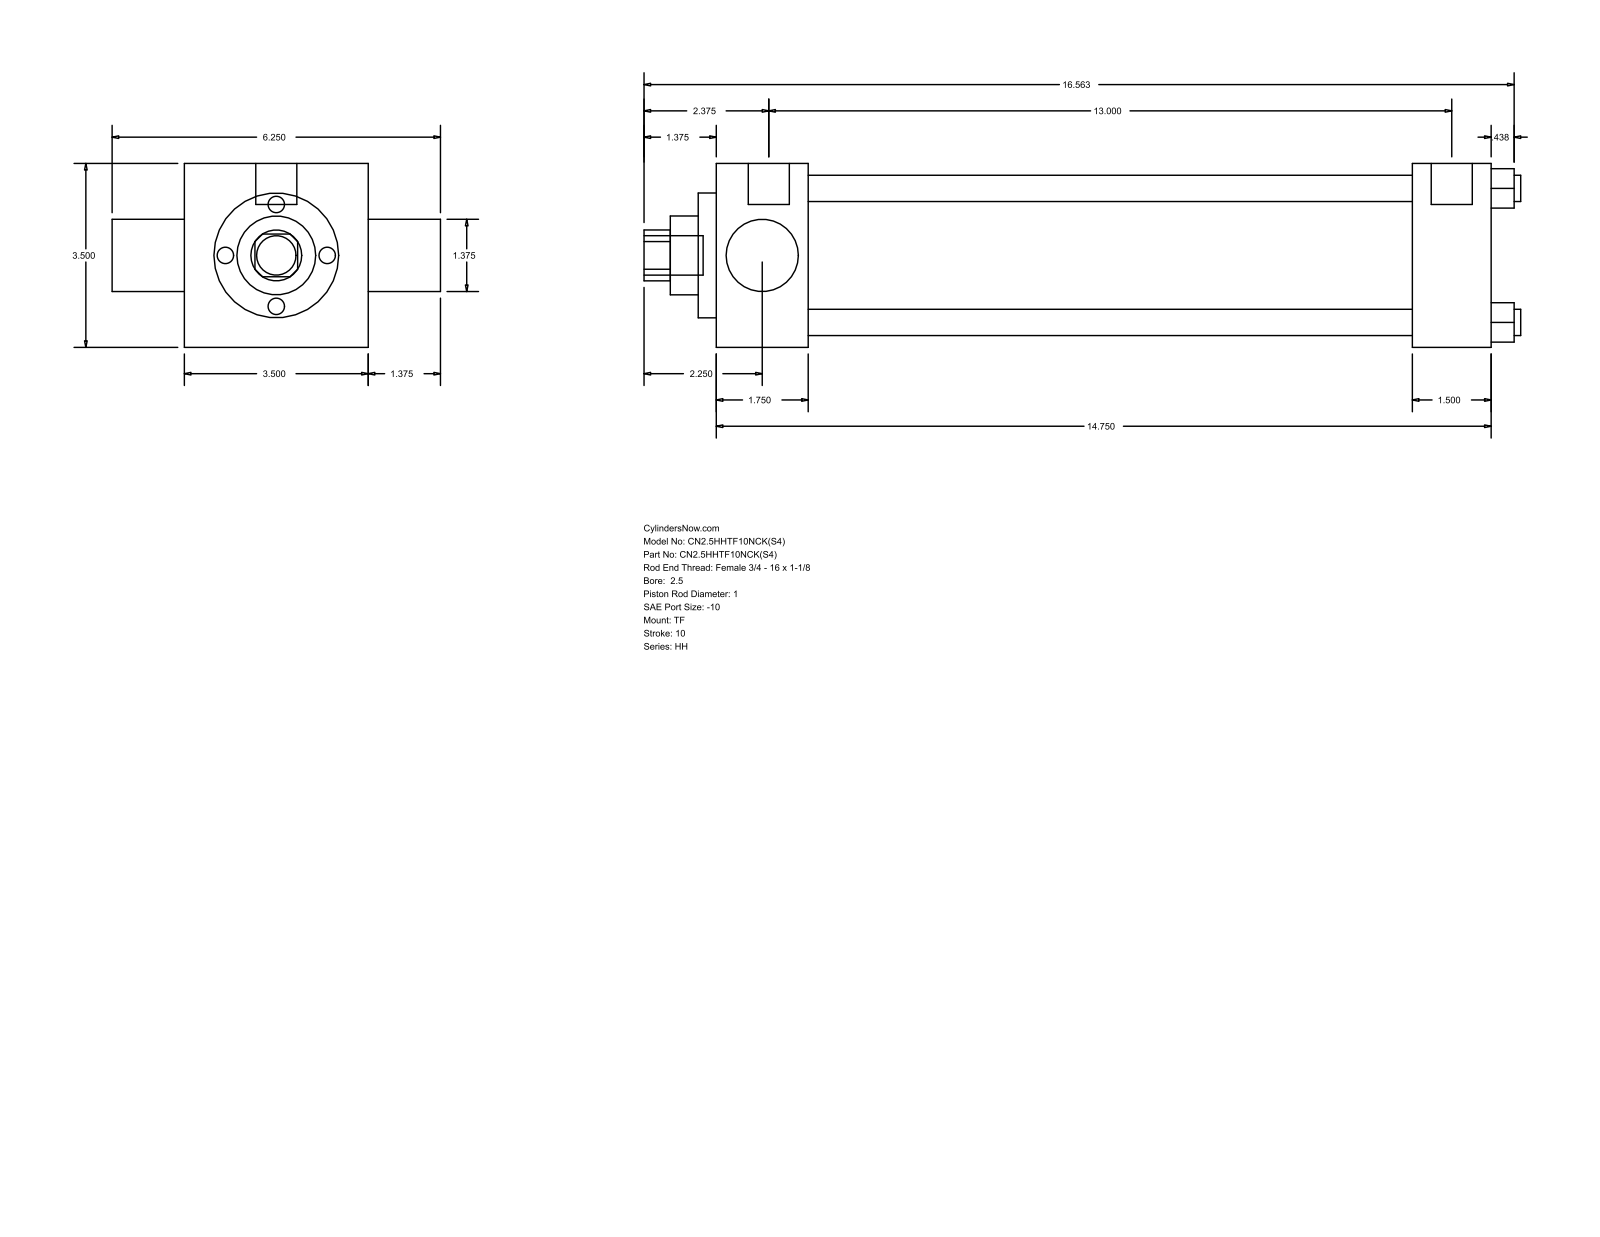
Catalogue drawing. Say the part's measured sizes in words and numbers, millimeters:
The part is named "HH_TF__0250_1". Its 3-D file was written by "GSSL Pune (CONFIG_CONTROL_DESIGN)". It is 0 solids with 86 faces: 61 planar, 25 cylindrical and 0 other. Overall it measures 423.86 by 158.75 by 88.9 millimeters. Round holes: 4 of diameter 12.7, 1 of diameter 25.4, 1 of diameter 34.92, 1 of diameter 38.1, 1 of diameter 60.33, 1 of diameter 73.03. Round bosses or shafts: 3 of diameter 5.56, 2 of diameter 19.84, 1 of diameter 19.05. Partial cylindrical surfaces (rounded edges, fillets, slot ends): 1 of radius 12.29. The main face-to-face distances are 88.9, 374.65, 44.46, 330.19, 336.56, 292.1, 38.09, 34.93, 123.83, 8.73. The hole center spacings are 45.79, 64.76, 91.58.
